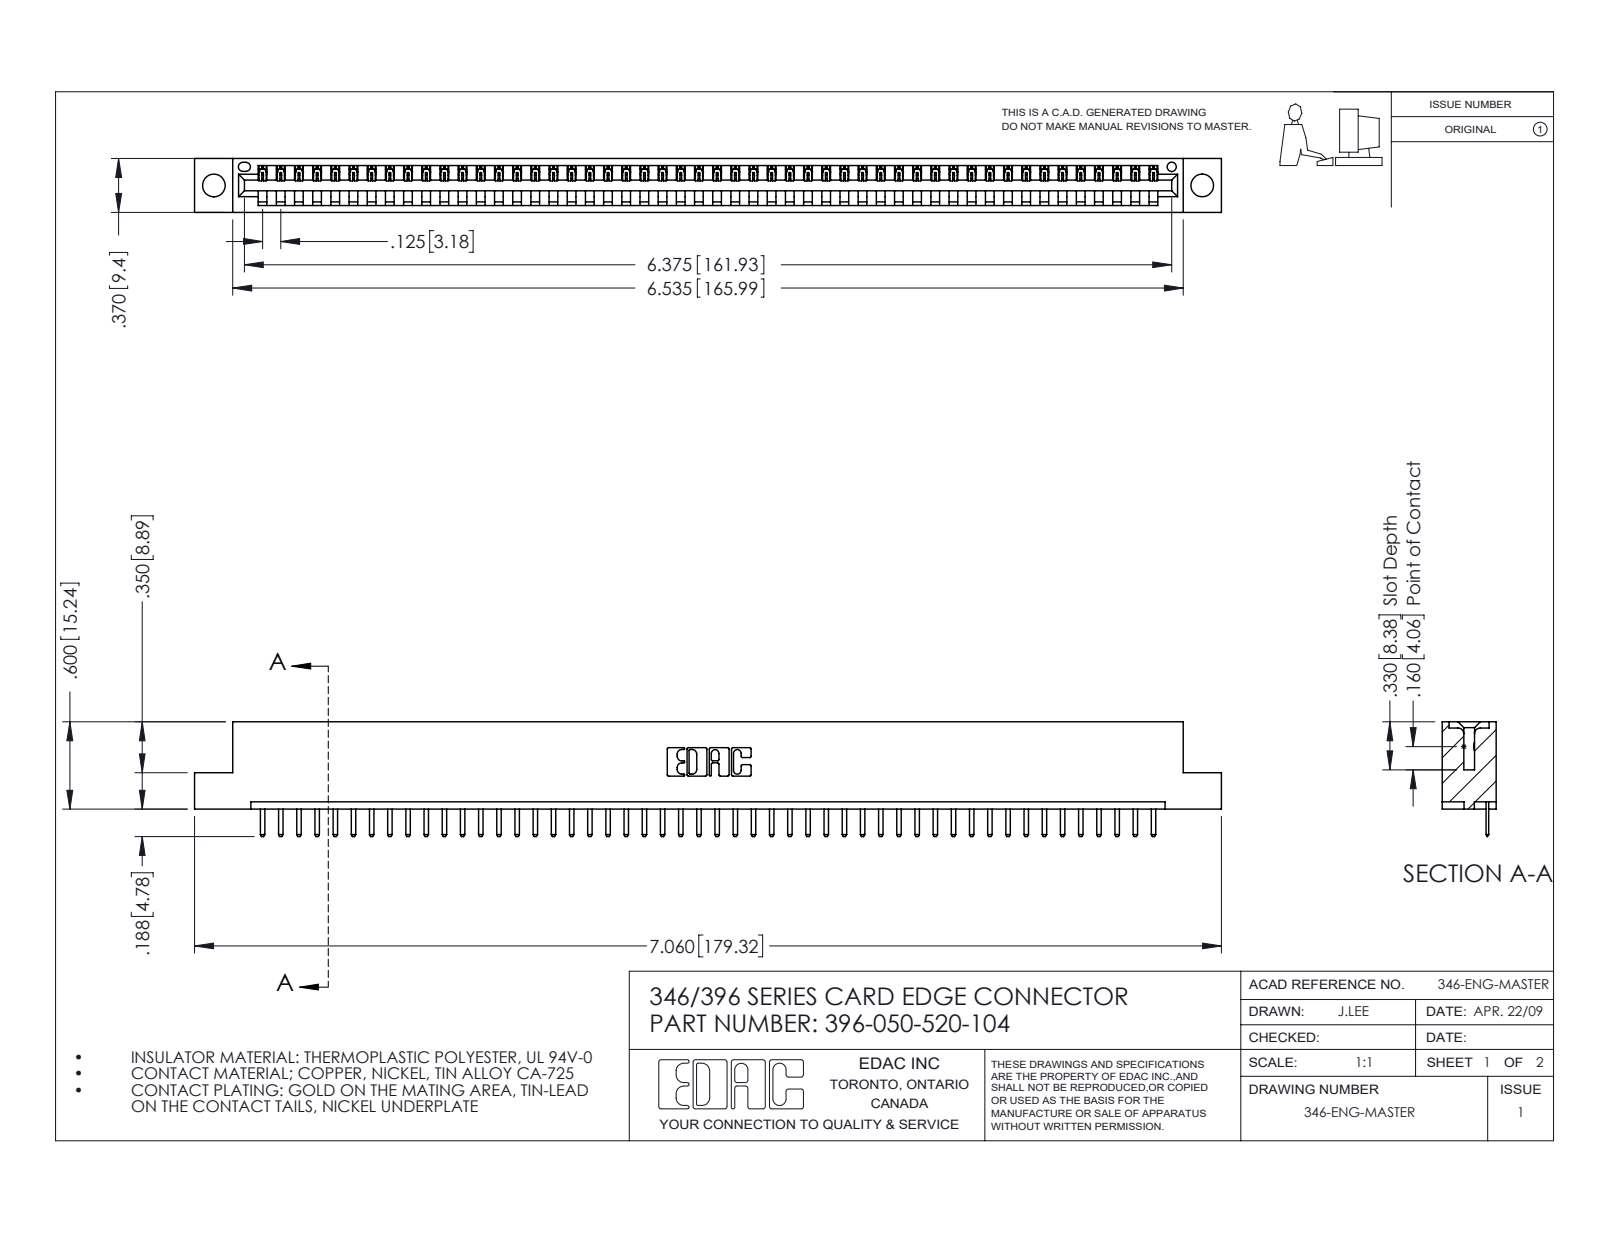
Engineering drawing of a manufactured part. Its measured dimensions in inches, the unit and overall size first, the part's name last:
Units: inches
Overall size (bounding box): 7.06 × 0.788 × 0.37
Round holes (diameter × count): ⌀0.156 ×2, ⌀0.064 ×1
Partial cylindrical surfaces — rounded edges, fillets, slot ends (radius × count): R0.01 ×102, R0.006 ×100, R0.01 ×22, R0.007 ×6, R0.031 ×6, R0.026 ×3, R0.031 ×2, R0.04 ×2
Main face-to-face distances: 0.048, 0.322, 0.37, 0.25, 0.148, 0.222, 0.1, 0.174, 0.072, 0.298
Hole centre spacings: 0.246, 6.586, 6.795
Volume: 1.037 in³ · Surface area: 32 in²
Bodies: 51 solids, 3222 faces (2176 planar, 1046 cylindrical, 0 other)
Part name (STEP PRODUCT): 396-050-520-104; 345-292-001_345-293-120; 346 Part_Flush Mounting Lugs - 0.156 Dia-TH
STEP written by: SolidWorks 2016 (CONFIG_CONTROL_DESIGN)
